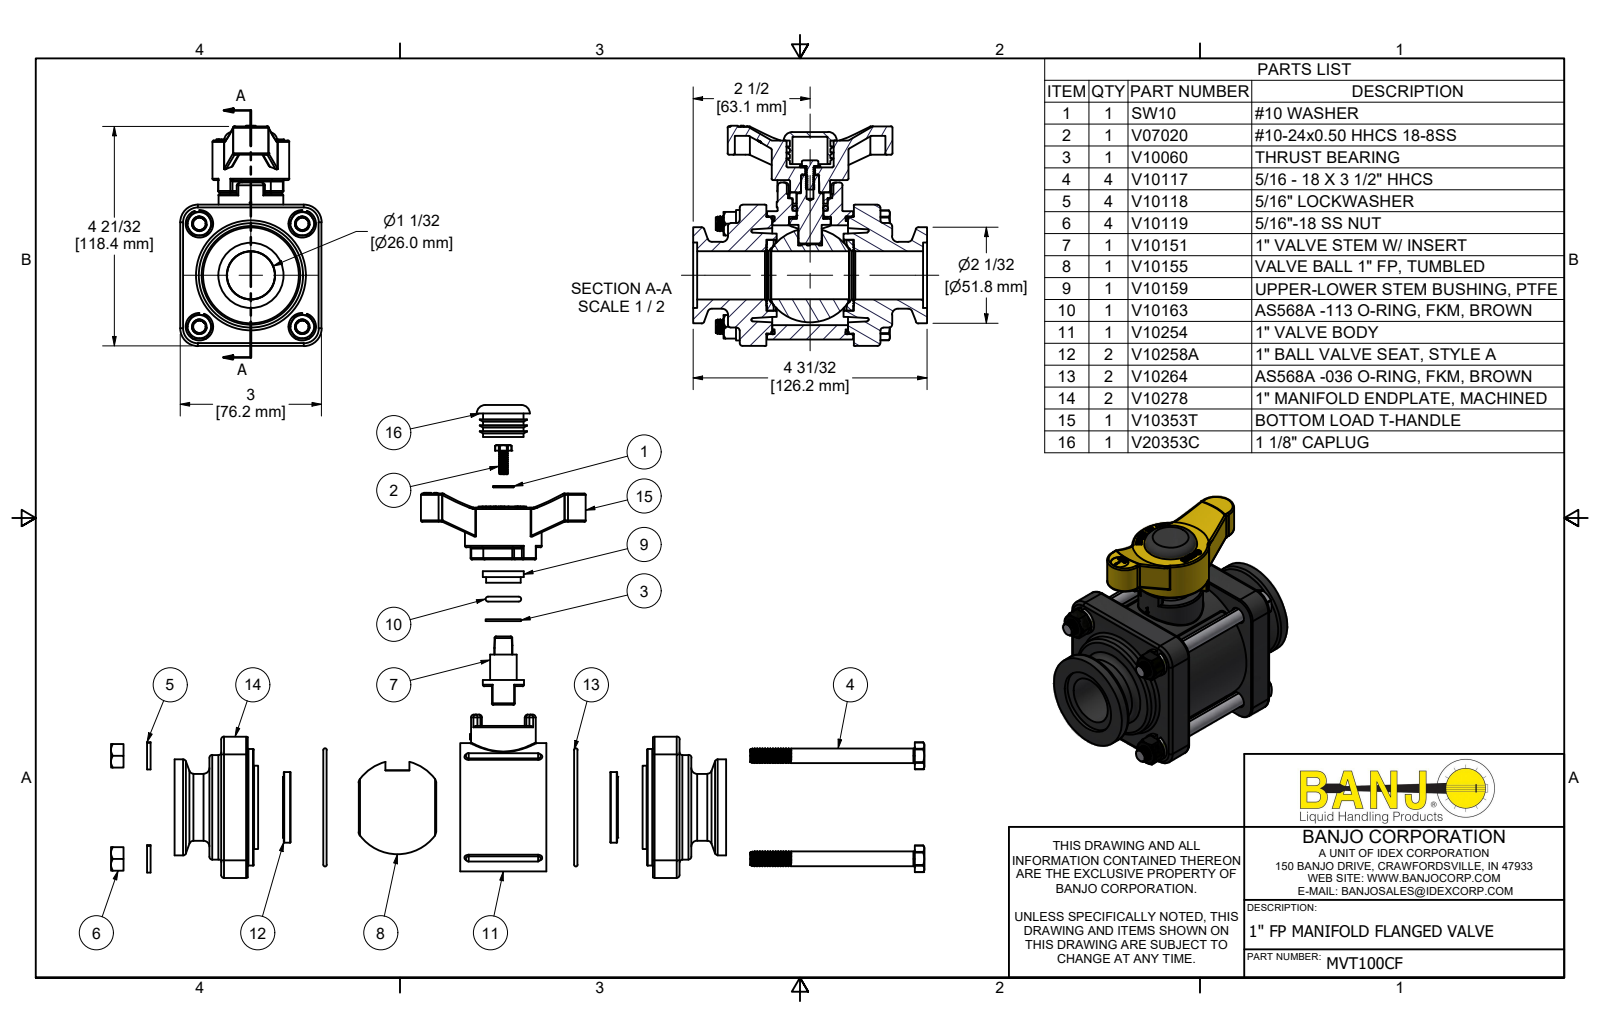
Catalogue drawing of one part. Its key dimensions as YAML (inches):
part_name: "MVT100CF; V10060; V10117; V10118 (+8 more)"
step_written_by: "Autodesk Inventor 2022 (AUTOMOTIVE_DESIGN)"
units: inches
bodies: {solids: 28, faces: 2098, planar: 692, cylindrical: 646, other: 760}
overall_size: [4.97, 4.677, 3]
volume: 23.73
surface_area: 209.8
round_holes:
  - {diameter: 0.252, count: 4}
  - {diameter: 0.322, count: 4}
  - {diameter: 0.36, count: 4}
  - {diameter: 0.091, count: 1}
  - {diameter: 0.128, count: 1}
  - {diameter: 0.145, count: 1}
  - {diameter: 0.203, count: 1}
  - {diameter: 0.21, count: 1}
  - {diameter: 0.375, count: 1}
  - {diameter: 0.562, count: 1}
  - {diameter: 0.572, count: 1}
  - {diameter: 0.575, count: 1}
round_bosses_or_shafts:
  - {diameter: 0.268, count: 60}
  - {diameter: 0.583, count: 4}
  - {diameter: 0.313, count: 4}
  - {diameter: 2.725, count: 1}
  - {diameter: 2.476, count: 1}
  - {diameter: 2.302, count: 1}
  - {diameter: 2.22, count: 1}
  - {diameter: 2.04, count: 1}
partial_cylinders:
  - {radius: 0.03, count: 74}
  - {radius: 0.06, count: 28}
  - {radius: 0.031, count: 12}
  - {radius: 0.062, count: 8}
  - {radius: 0.134, count: 8}
  - {radius: 0.375, count: 6}
  - {radius: 0.078, count: 4}
  - {radius: 0.284, count: 4}
face_to_face_distances: [0.565, 2.425, 0.125, 0.69, 2.3, 1.735, 3, 2.99, 0.99, 1.555]
hole_center_spacings: [1.547, 2.188, 3.094, 0.663, 1.533, 1.83]
